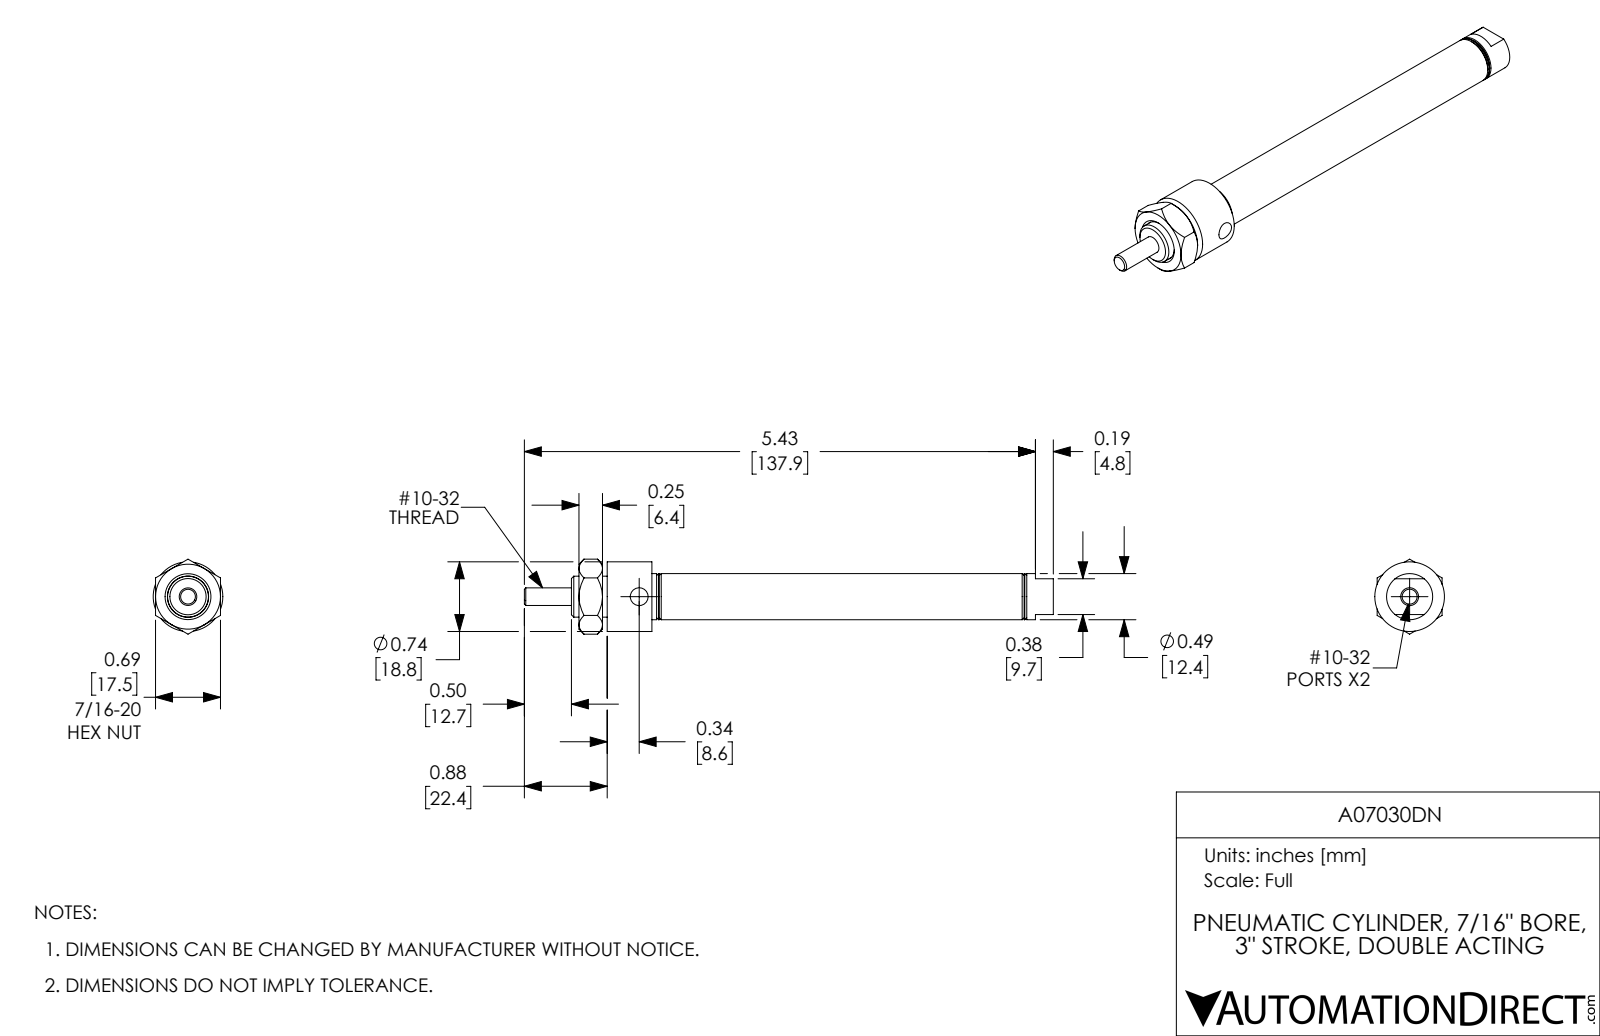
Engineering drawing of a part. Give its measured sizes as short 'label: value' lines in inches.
name: A07030DN; A07030DN-Rod; A07030DN_Mounting Nut_D-154; A07030DN-MainBody
written by: SolidWorks 2017 (AUTOMOTIVE_DESIGN)
unit: in
bodies: 3 solids, 92 faces (28 planar, 32 cylindrical, 32 other)
size: 5.62 × 0.797 × 0.74
volume: 0.743 in³; area: 20.3 in²
holes: 2× ⌀0.159, 2× ⌀0.19, 1× ⌀0.187, 1× ⌀0.437
bosses: 1× ⌀0.74, 1× ⌀0.49, 1× ⌀0.435
face distances: 4.12, 0.62, 0.69, 3.645, 0.475, 0.05, 0.525, 4.42, 0.775, 0.3
